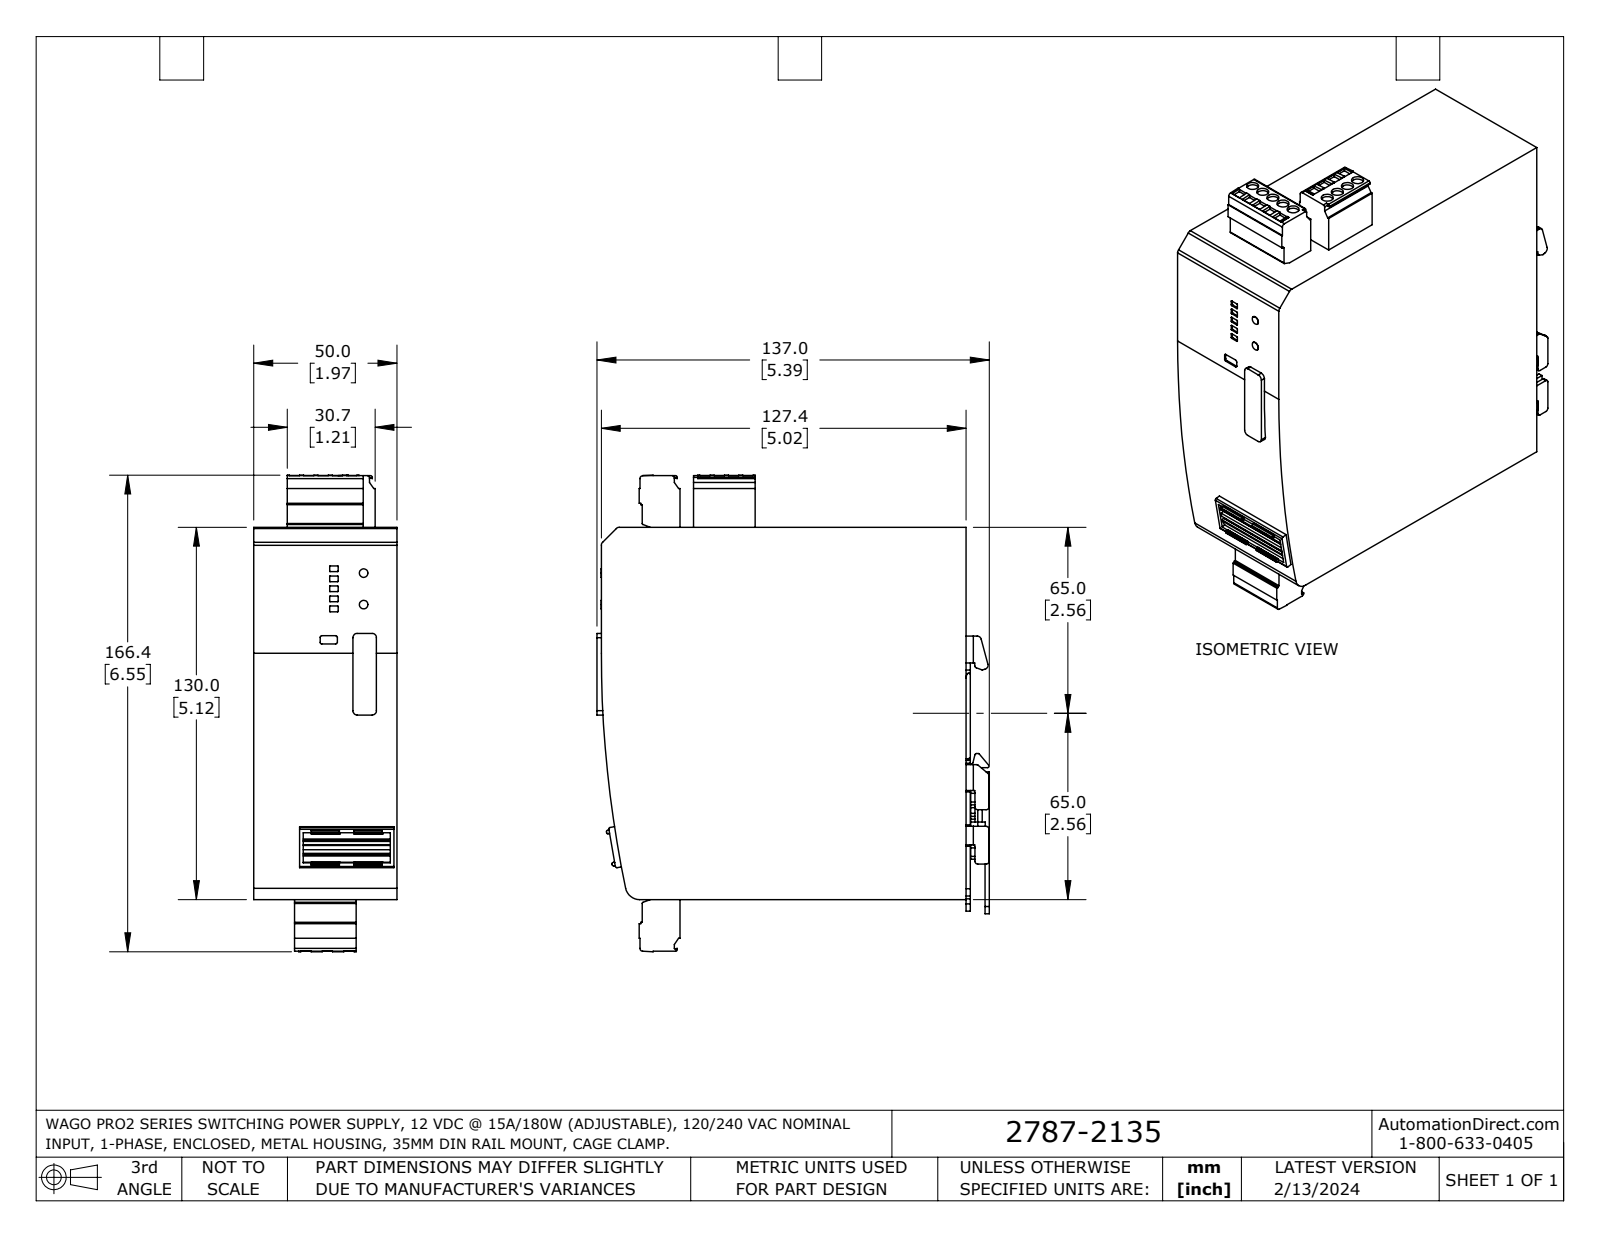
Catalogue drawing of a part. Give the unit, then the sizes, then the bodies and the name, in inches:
Units: inches
Overall size (bounding box): 6.551 × 5.394 × 1.969
Round holes (diameter × count): ⌀0.165 ×12
Round bosses / shafts (diameter × count): ⌀0.118 ×2
Partial cylindrical surfaces — rounded edges, fillets, slot ends (radius × count): R0.039 ×43, R0.008 ×31, R0.02 ×19, R0.098 ×16, R0.024 ×10, R0.03 ×6, R0.059 ×6, R0.028 ×4
Main face-to-face distances: 1.969, 5.118, 0.059, 5.075, 0.26, 5.016, 5.335, 0.201, 5.276, 0.319
Hole centre spacings: 0.197, 0.394, 0.591, 0.039, 0.157, 0.295, 0.059, 0.138
Volume: 51.26 in³ · Surface area: 106.9 in²
Bodies: 1 solid, 568 faces (370 planar, 198 cylindrical, 0 other)
Part name (STEP PRODUCT): 2787-2135
STEP written by: SolidWorks 2023 (AUTOMOTIVE_DESIGN)
